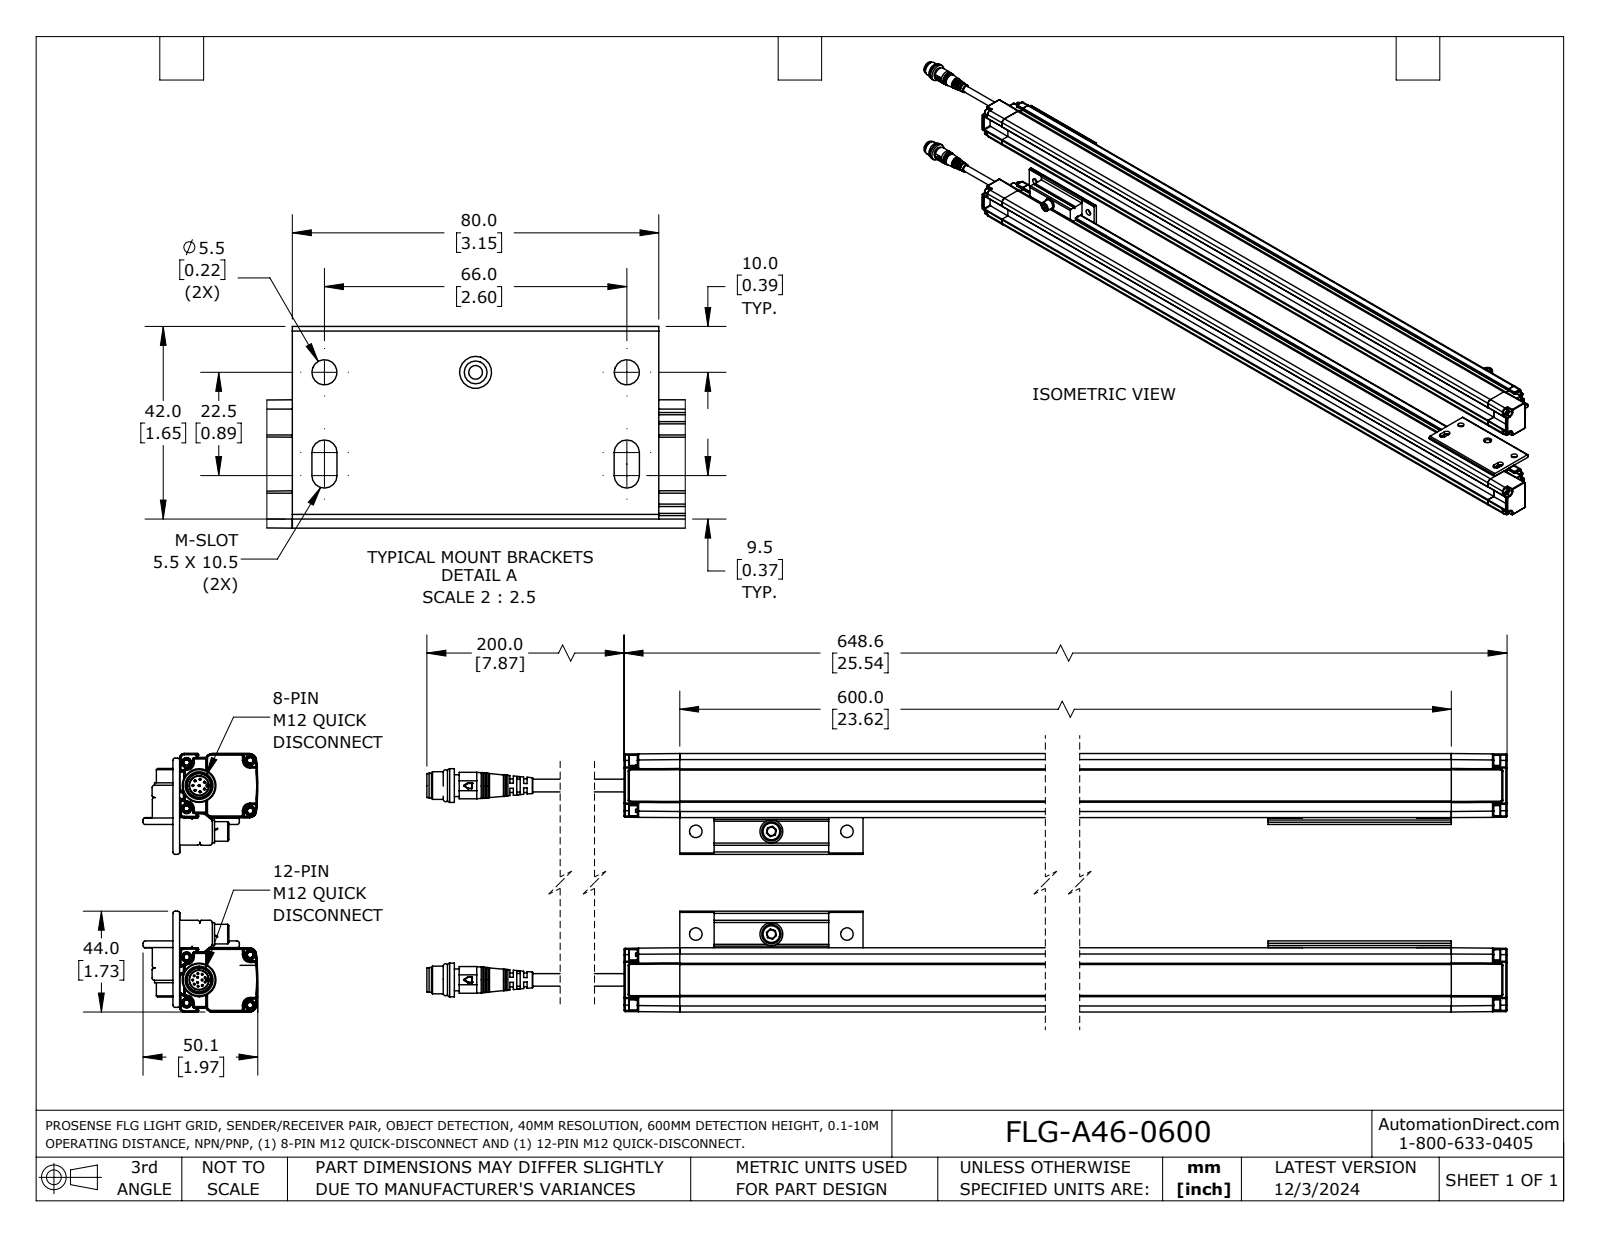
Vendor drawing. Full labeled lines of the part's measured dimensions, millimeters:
Part name (STEP PRODUCT): FLG-A46-0600
STEP written by: SolidWorks 2023 (AUTOMOTIVE_DESIGN)
Units: millimetres
Bodies: 5 solids, 860 faces (426 planar, 238 cylindrical, 196 other)
Overall size (bounding box): 740.6 × 50.1 × 44
Volume: 539 300 mm³ · Surface area: 142 600 mm²
Round holes (diameter × count): ⌀0.4 ×16, ⌀5.5 ×4, ⌀2.5 ×2, ⌀5 ×2, ⌀8.3 ×1
Round bosses / shafts (diameter × count): ⌀0.8 ×8, ⌀4.5 ×4, ⌀3 ×4, ⌀10 ×2, ⌀8.5 ×2, ⌀5.5 ×2, ⌀3.7 ×2, ⌀1.5 ×2
Partial cylindrical surfaces — rounded edges, fillets, slot ends (radius × count): R0.5 ×76, R1 ×20, R0.3 ×10, R2.7 ×8, R0.2 ×6, R0.3 ×6, R2.5 ×4, R1.2 ×2
Main face-to-face distances: 28, 1.8, 20.8, 7.2, 24.6, 3, 26.4, 4.8, 5.5, 26.2
Hole centre spacings: 2.7, 4.1, 33, 5.5, 2.3, 2.3, 2.3, 3
